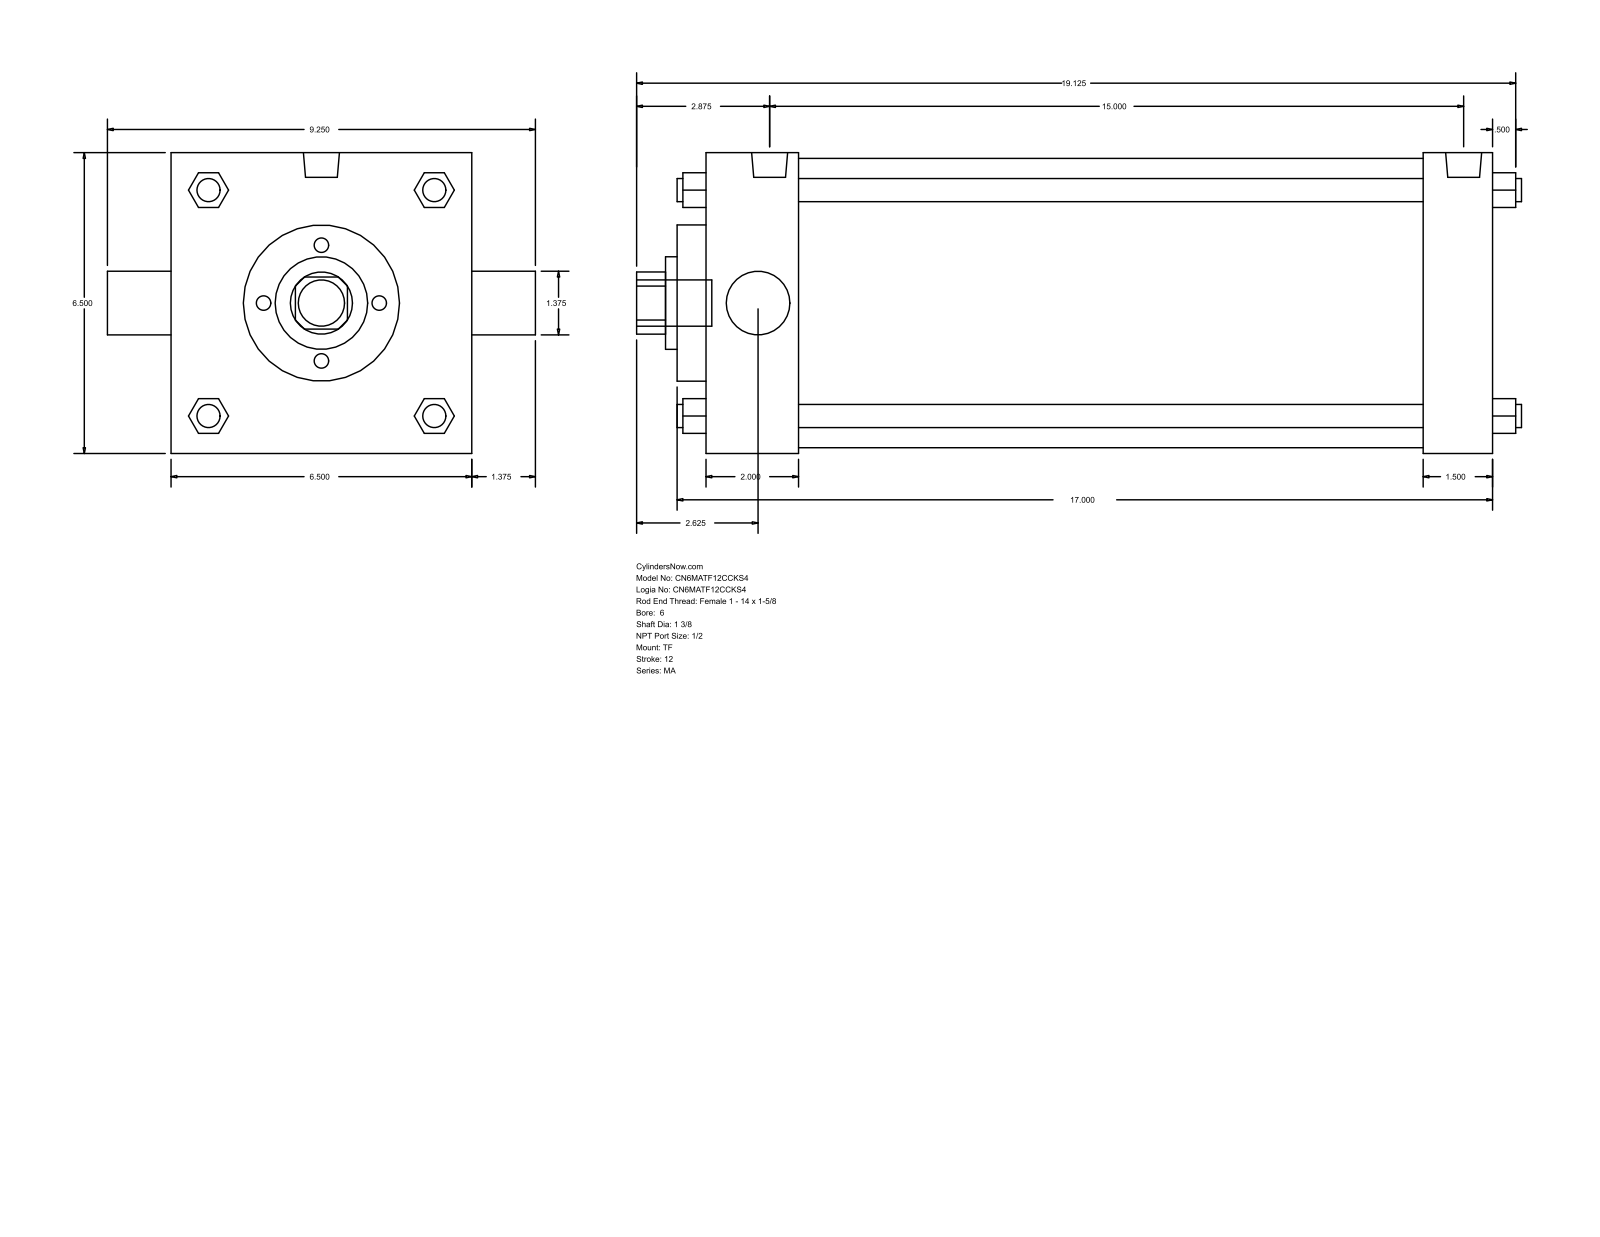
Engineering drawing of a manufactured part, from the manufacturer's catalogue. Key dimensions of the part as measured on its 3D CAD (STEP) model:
Part name (STEP PRODUCT): MA_TF__0600_1.375
STEP written by: GSSL Pune (CONFIG_CONTROL_DESIGN)
Units: millimetres
Bodies: 0 solids, 122 faces (93 planar, 29 cylindrical, 0 other)
Overall size (bounding box): 485.77 × 234.95 × 165.1
Round holes (diameter × count): ⌀34.92 ×2, ⌀50.8 ×1, ⌀85.72 ×1, ⌀158.75 ×1
Round bosses / shafts (diameter × count): ⌀12.7 ×4, ⌀17.46 ×3, ⌀19.77 ×2, ⌀25.4 ×1
Partial cylindrical surfaces — rounded edges, fillets, slot ends (radius × count): R17.06 ×1
Main face-to-face distances: 165.1, 434.97, 50.8, 384.17, 396.88, 346.08, 38.09, 15.87, 66.67, 412.75
